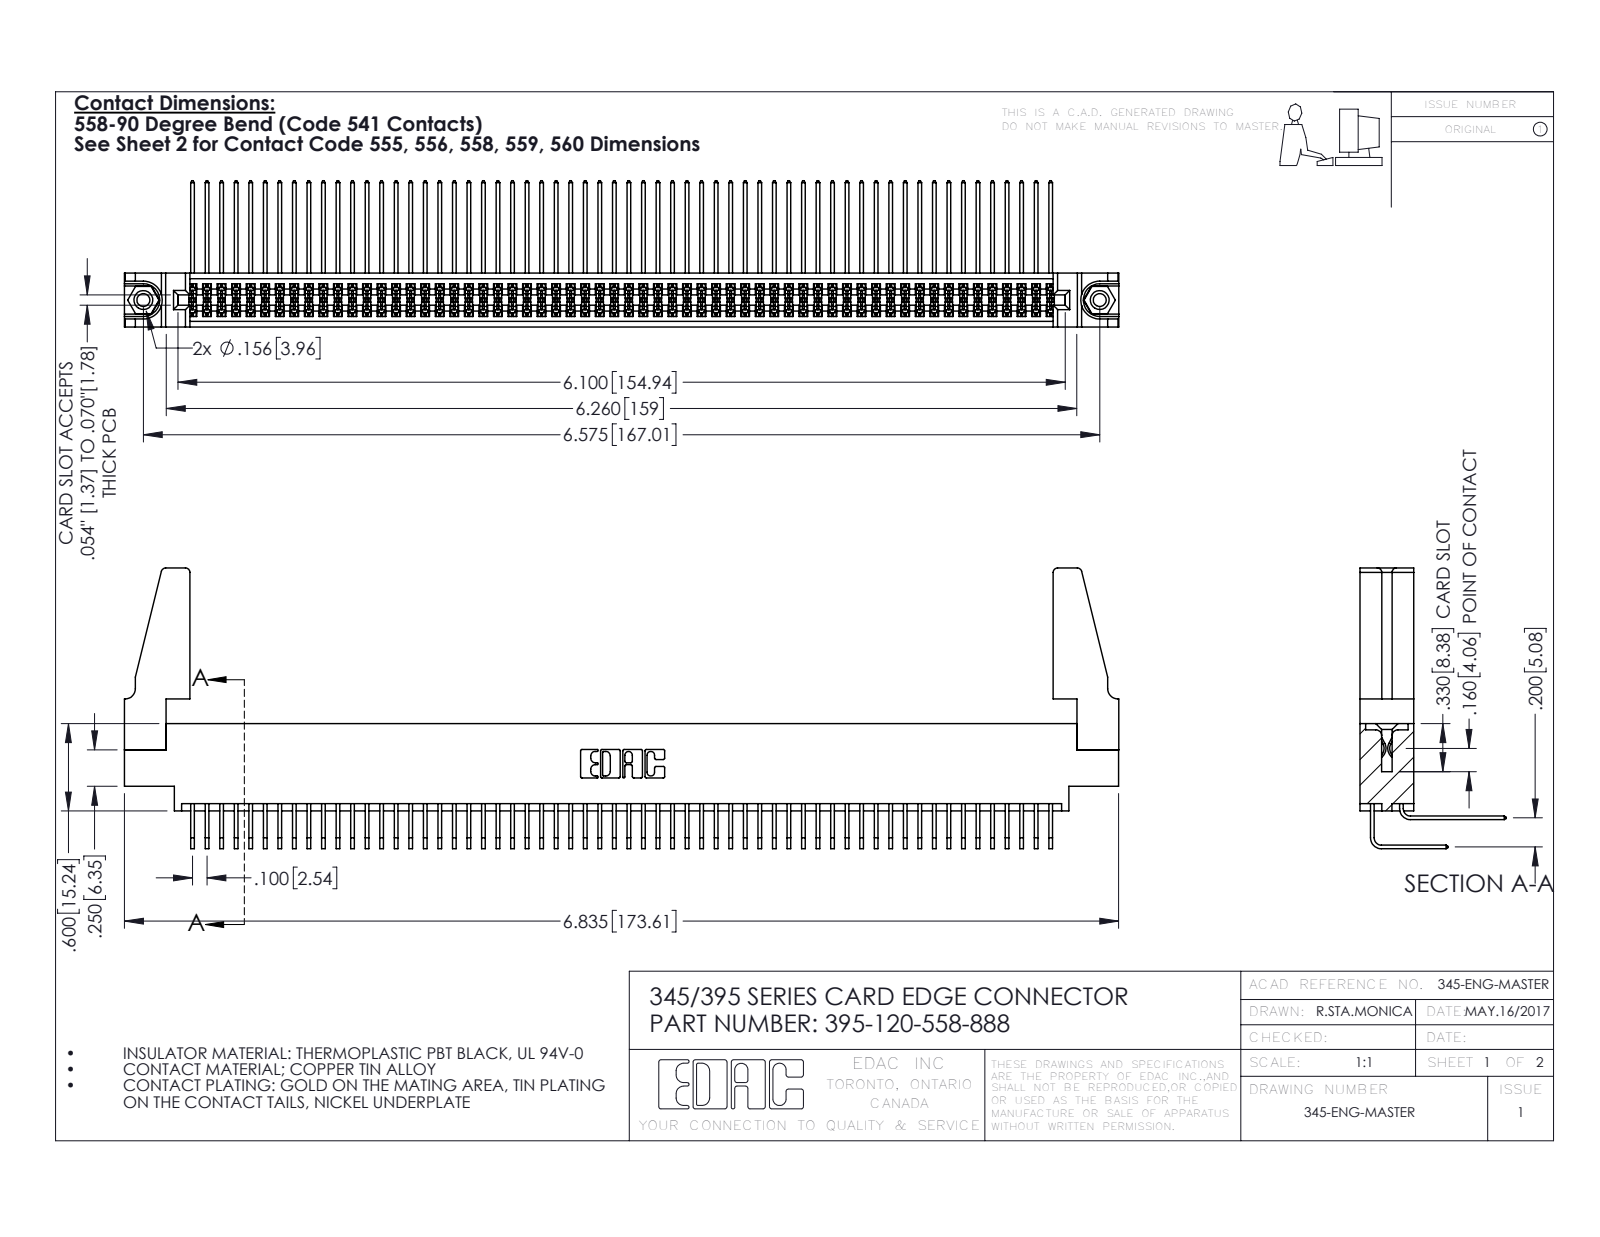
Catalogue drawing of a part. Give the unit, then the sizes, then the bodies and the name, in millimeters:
Units: millimetres
Overall size (bounding box): 173.6 × 49 × 25.5
Round holes (diameter × count): ⌀2.3 ×2, ⌀3.2 ×2, ⌀4 ×2, ⌀1.6 ×1
Round bosses / shafts (diameter × count): ⌀3.9 ×2
Partial cylindrical surfaces — rounded edges, fillets, slot ends (radius × count): R0.2 ×181, R0.3 ×22, R0.8 ×8, R0.2 ×6, R0.8 ×6, R0.7 ×3, R0.4 ×2, R0.5 ×2
Main face-to-face distances: 1.8, 7.6, 5.1, 9.4, 2.5, 6.9, 0.6, 5.7, 4.4, 0.6
Hole centre spacings: 6.9, 161, 167
Volume: 20 860 mm³ · Surface area: 32 900 mm²
Bodies: 125 solids, 6494 faces (4356 planar, 2122 cylindrical, 16 other)
Part name (STEP PRODUCT): 345-292-001_558 Tail - 2; 345-292-001_558 559 Tail - 1; 395-120-558-888; 345 Part_0.170 Offset - 0.156 Dia-TH (+2 more)
STEP written by: SolidWorks 2016 (CONFIG_CONTROL_DESIGN)
